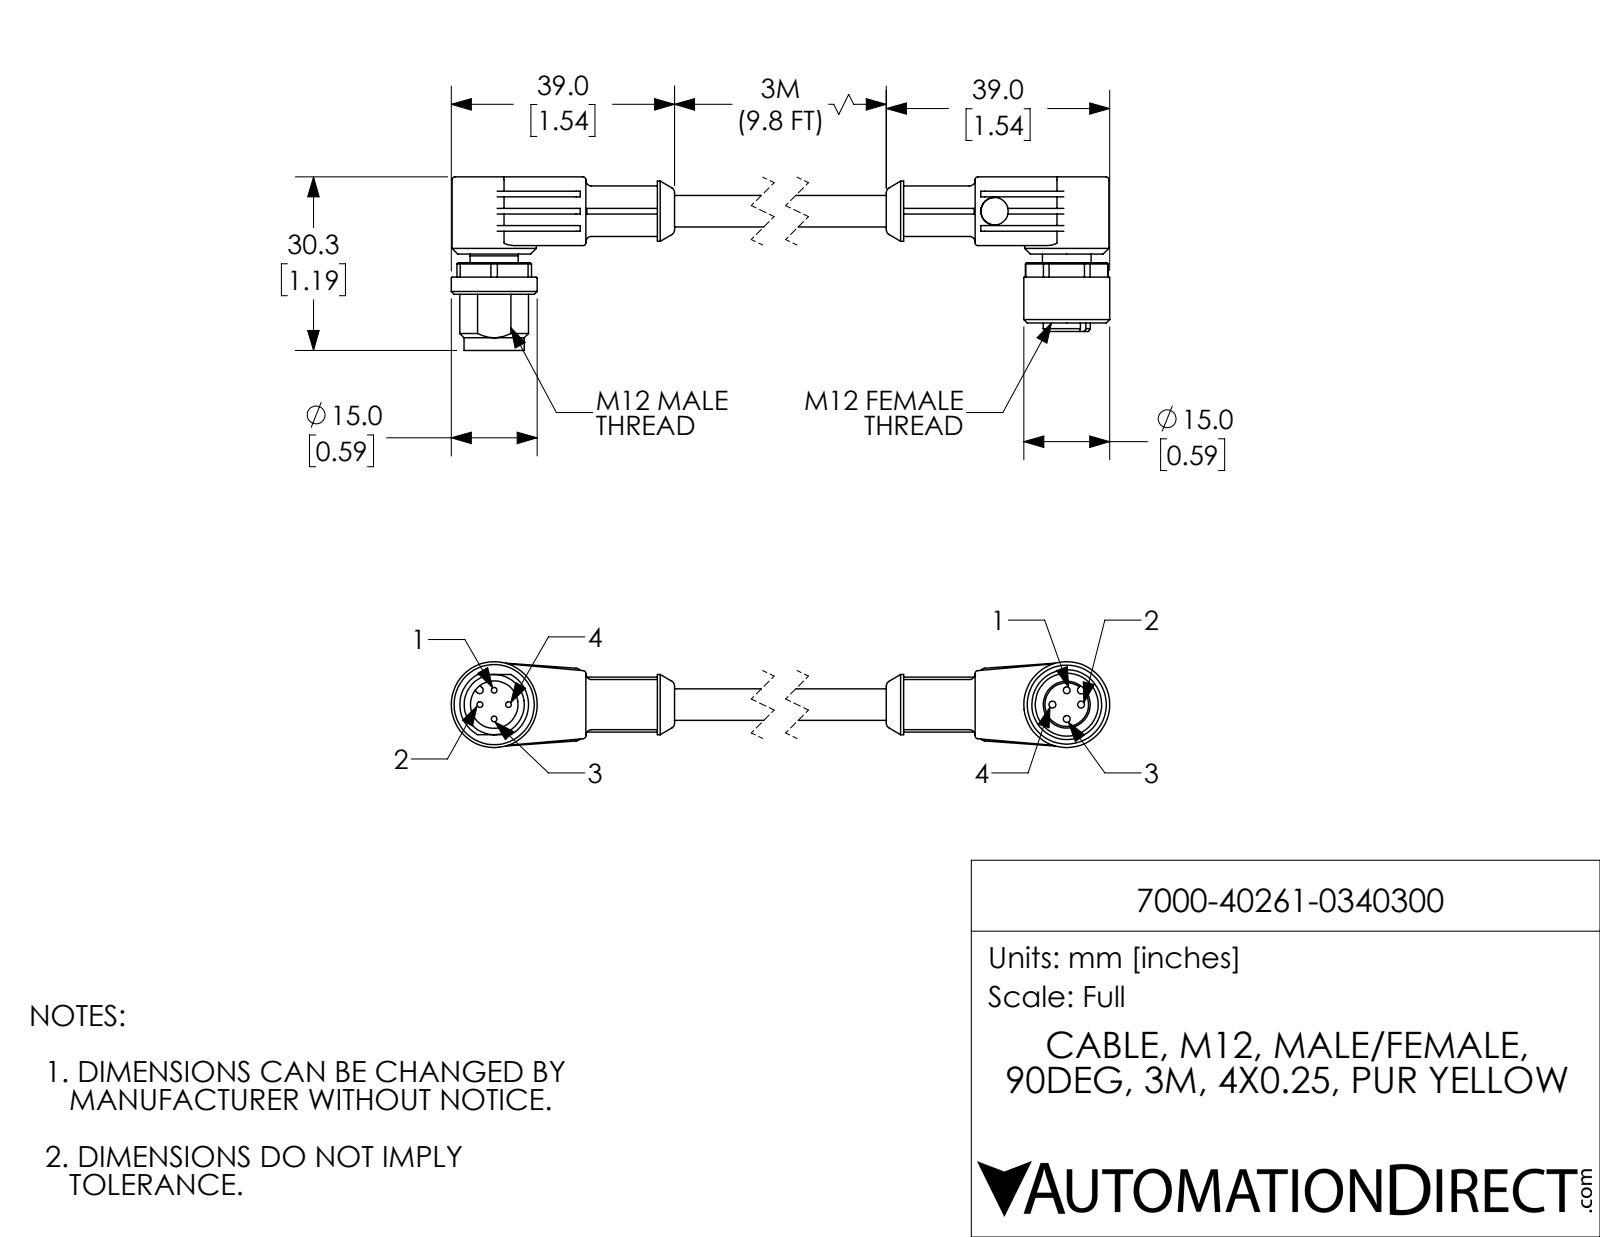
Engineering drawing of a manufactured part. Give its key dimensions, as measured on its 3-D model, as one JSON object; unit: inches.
{"part_name": "7000-40261-0340300_FEMALE; 7000-40261-0340300; 7000-40261-0340300_MALE", "step_written_by": "SolidWorks 2021 (CONFIG_CONTROL_DESIGN)", "units": "inches", "bodies": {"solids": 2, "faces": 290, "planar": 123, "cylindrical": 104, "other": 63}, "overall_size": [5.118, 1.193, 0.591], "volume_in3": 0.829, "surface_area_in2": 10.88, "round_holes": [[0.047, 4], [0.189, 2], [0.327, 1], [0.433, 1]], "round_bosses_or_shafts": [[0.039, 4], [0.591, 2], [0.579, 2], [0.413, 2], [0.346, 1], [0.335, 1], [0.333, 1], [0.331, 1]], "partial_cylinders_radius": [[0.02, 16], [0.039, 4], [0.283, 2], [0.024, 1], [0.026, 1], [0.236, 1]], "face_to_face_distances": [0.472, 0.059, 0.118, 0.591, 0.531, 0.178, 0.217, 0.098, 0.374, 0.256], "hole_center_spacings": [0.098, 0.139, 0.197, 4.529, 3.563, 4.429, 4.528, 4.626]}
